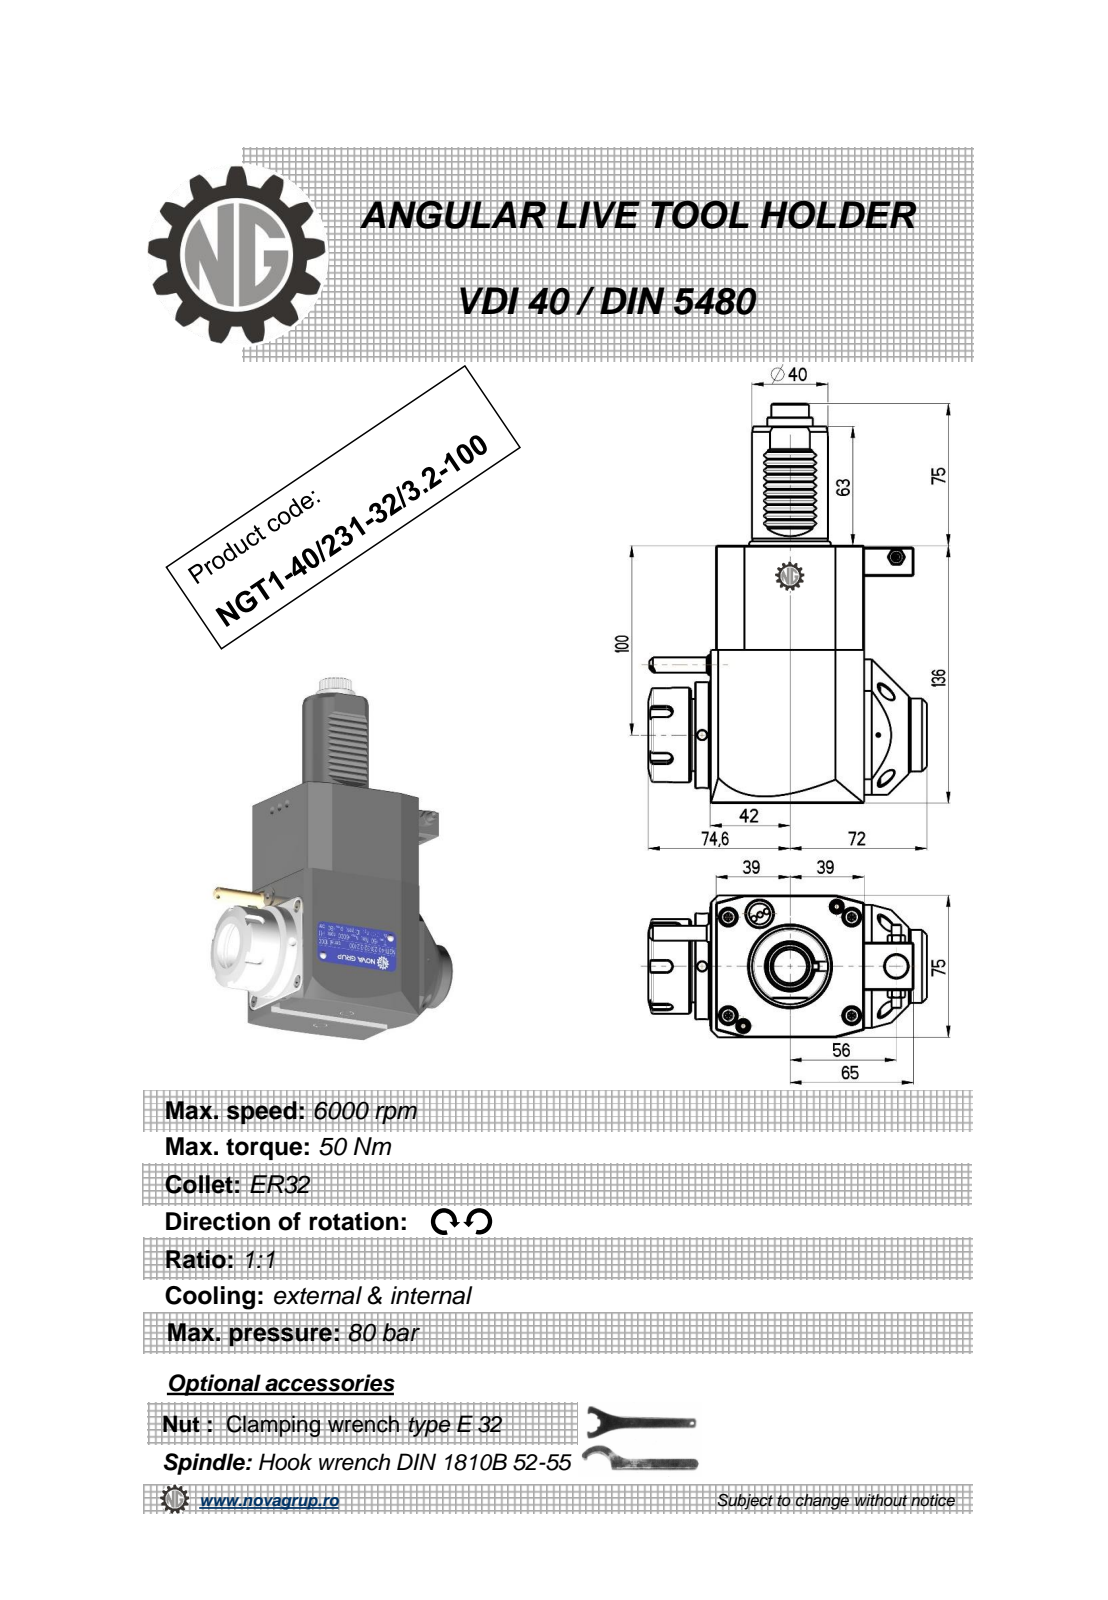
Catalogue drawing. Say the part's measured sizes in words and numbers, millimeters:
The part is named "NGT1_40_231_32_3_2_100". Its 3-D file was written by "PRO/ENGINEER BY PARAMETRIC TECHNOLOGY CORPORATION, 2010280 (CONFIG_CONTROL_DESIGN)". It is 1 solid with 537 faces: 193 planar, 183 cylindrical and 161 other. Overall it measures 211 by 146.6 by 75 millimeters. Its volume is 1 028 000 cubic millimeters and its surface area 78 944 square millimeters. Round holes: 3 of diameter 5, 1 of diameter 3, 1 of diameter 4.2, 1 of diameter 9.5, 1 of diameter 12, 1 of diameter 27. Round bosses or shafts: 1 of diameter 56, 1 of diameter 50, 1 of diameter 43, 1 of diameter 40, 1 of diameter 38.5, 1 of diameter 24, 1 of diameter 11.2, 1 of diameter 8.96. Partial cylindrical surfaces (rounded edges, fillets, slot ends): 48 of radius 2.08, 12 of radius 0.26, 10 of radius 0.3, 6 of radius 0.22, 5 of radius 3, 1 of radius 9.08, 1 of radius 9.92, 1 of radius 15. The main face-to-face distances are 75, 136, 78, 81, 3, 84.88, 7.5, 2.8, 80.8, 0.5. The hole center spacings are 40.93, 57.24, 91.5, 102.25, 138.89.
